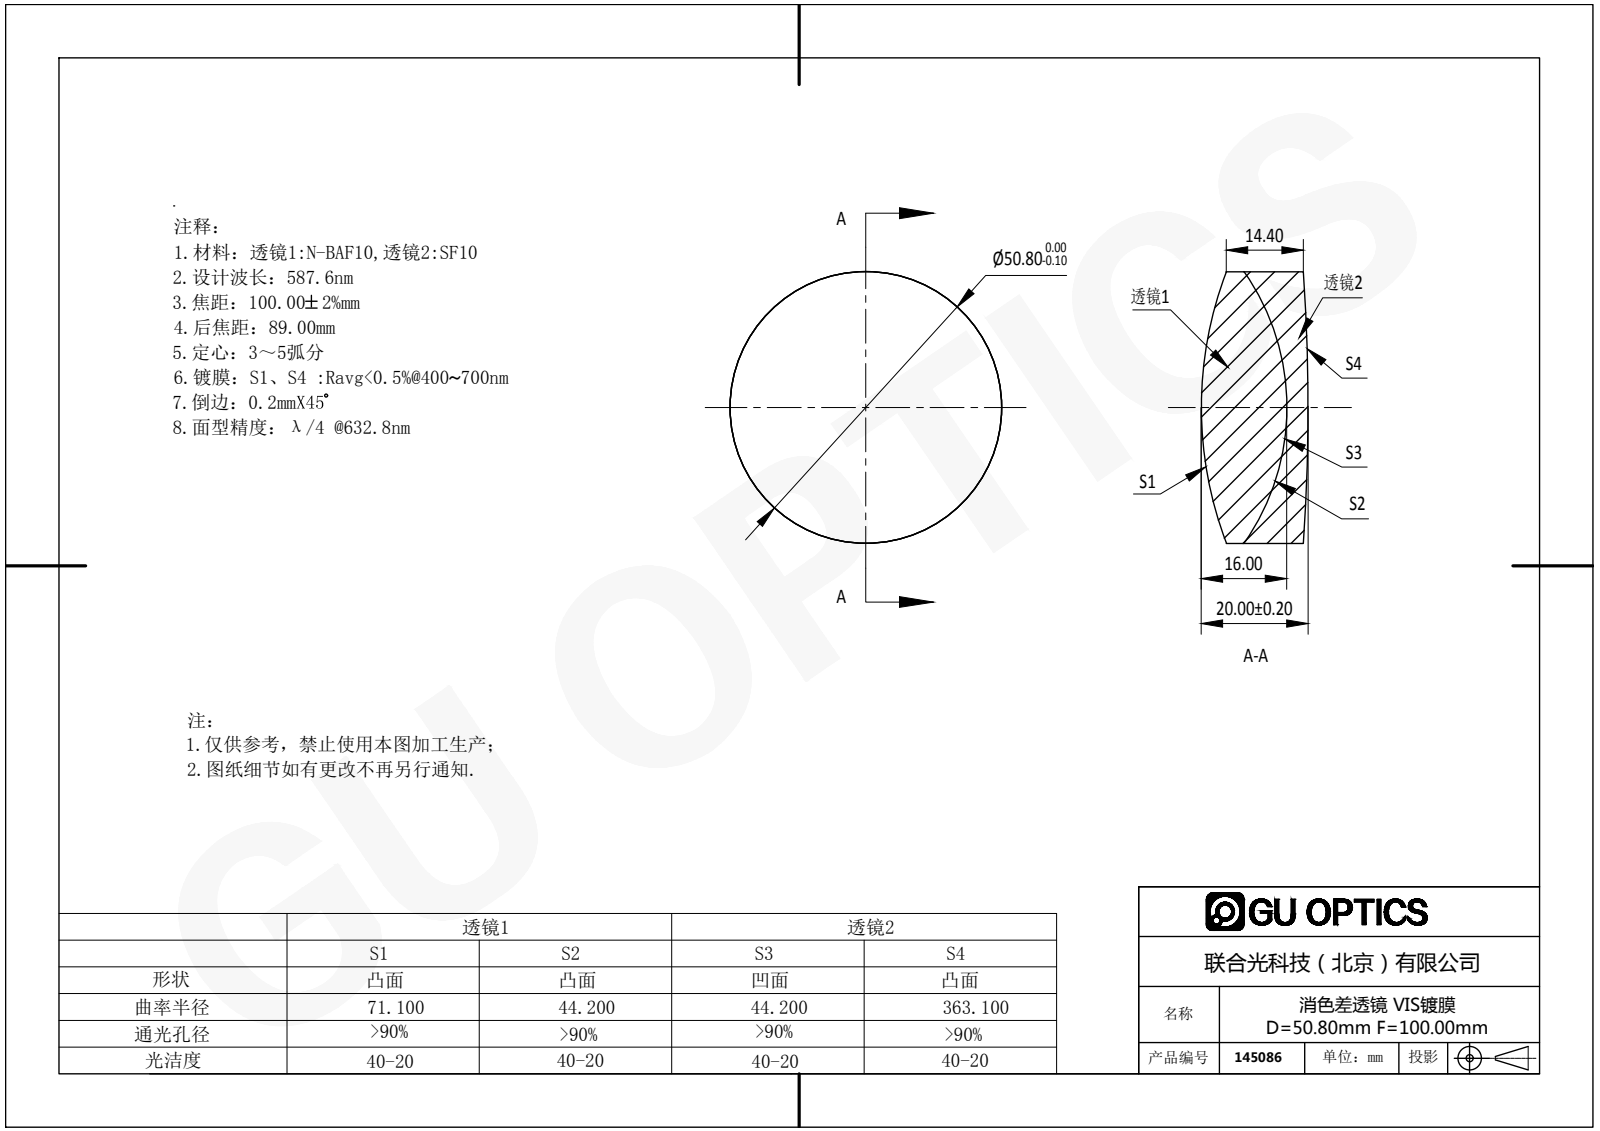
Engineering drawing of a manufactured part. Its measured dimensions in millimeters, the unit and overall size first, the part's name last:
Units: millimetres
Overall size (bounding box): 50.8 × 50.8 × 20
Round bosses / shafts (diameter × count): ⌀50.8 ×1
Volume: 34 935 mm³ · Surface area: 10 885 mm²
Bodies: 2 solids, 12 faces (0 planar, 4 cylindrical, 8 other)
Part name (STEP PRODUCT): 145086
STEP written by: SolidWorks 2016 (AUTOMOTIVE_DESIGN)
